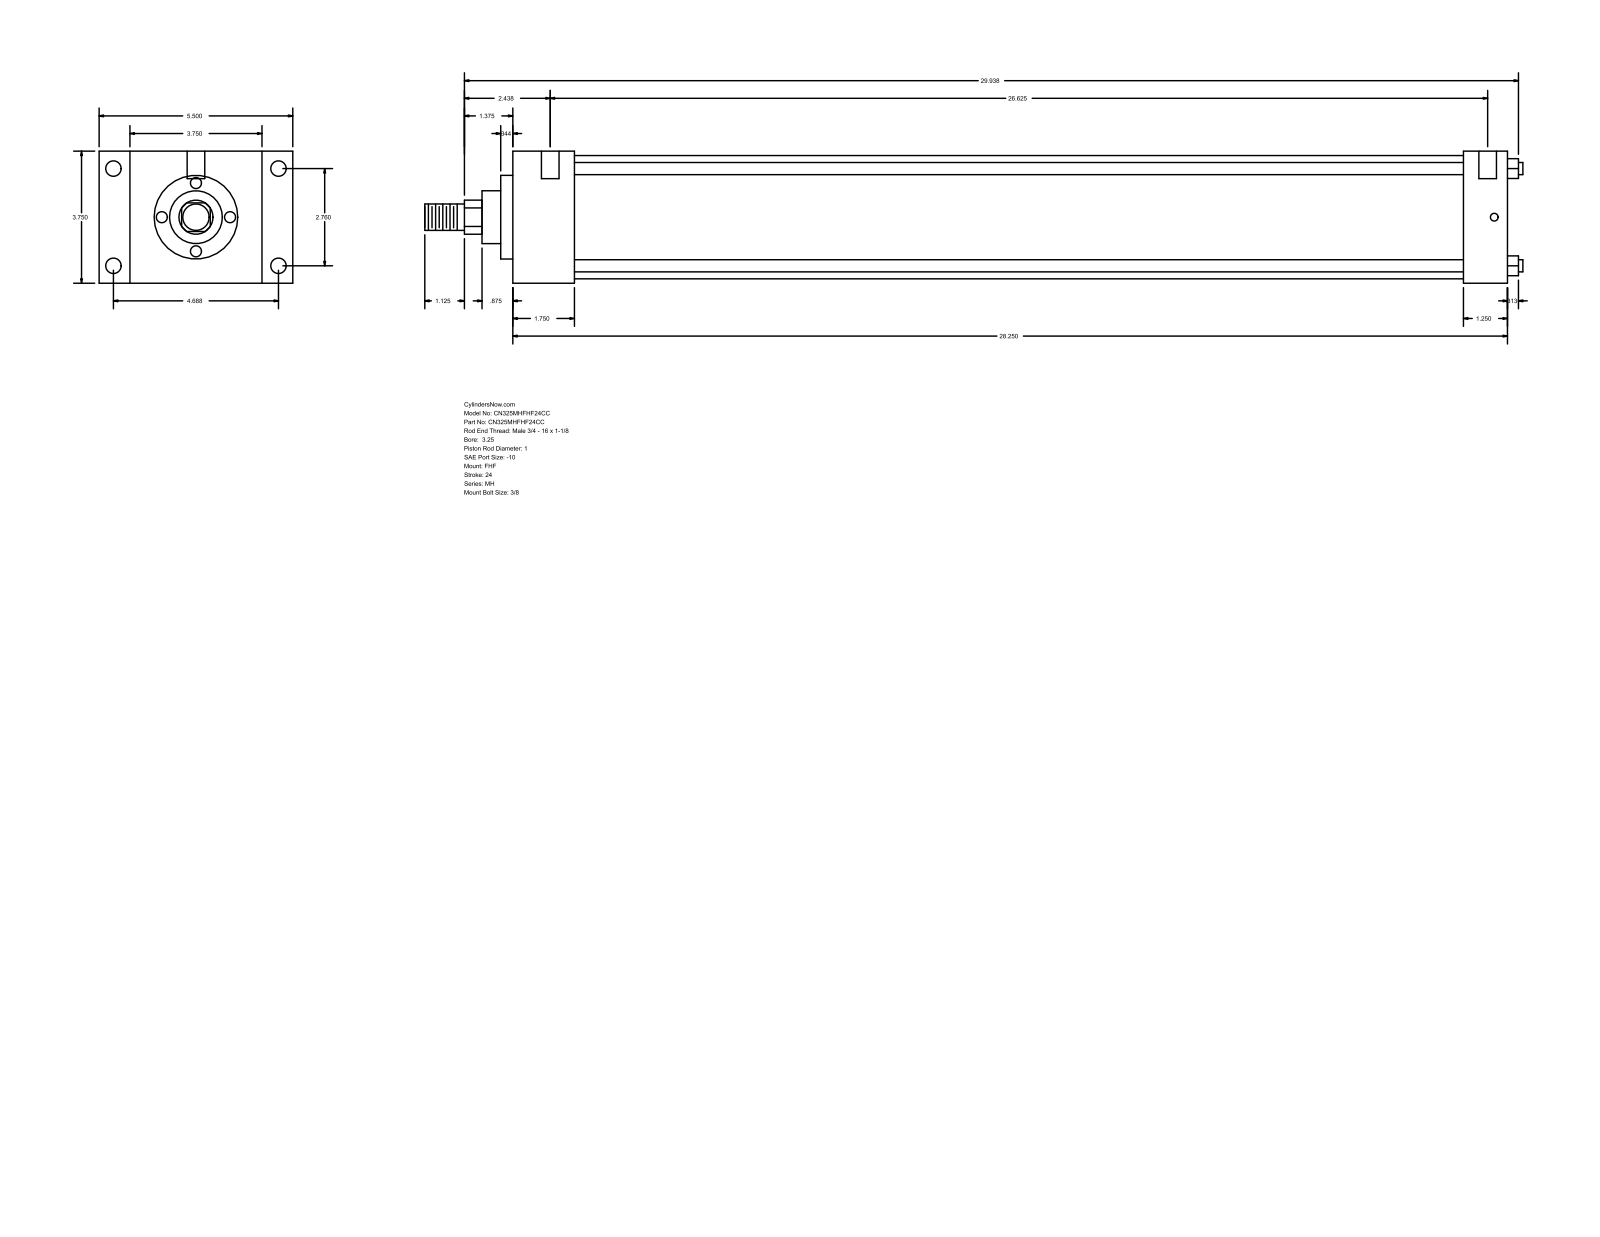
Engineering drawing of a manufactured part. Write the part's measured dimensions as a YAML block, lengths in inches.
part_name: "MH_FHF__0325_1"
step_written_by: "GSSL Pune (CONFIG_CONTROL_DESIGN)"
units: inches
bodies: {solids: 0, faces: 90, planar: 61, cylindrical: 29, other: 0}
overall_size: [31.187, 5.5, 3.75]
round_holes:
  - {diameter: 0.219, count: 4}
  - {diameter: 0.438, count: 4}
  - {diameter: 0.5, count: 2}
round_bosses_or_shafts:
  - {diameter: 0.345, count: 4}
  - {diameter: 3.5, count: 1}
  - {diameter: 2.375, count: 1}
  - {diameter: 1.5, count: 1}
  - {diameter: 1, count: 1}
  - {diameter: 0.75, count: 1}
partial_cylinders:
  - {radius: 0.484, count: 1}
face_to_face_distances: [3.75, 28.25, 1.75, 26.5, 0.875, 4.625, 5.5, 27, 25.25, 1.25]
hole_center_spacings: [2.76, 4.687, 5.439, 26.875, 0.062, 0.187, 26.625, 26.687]
